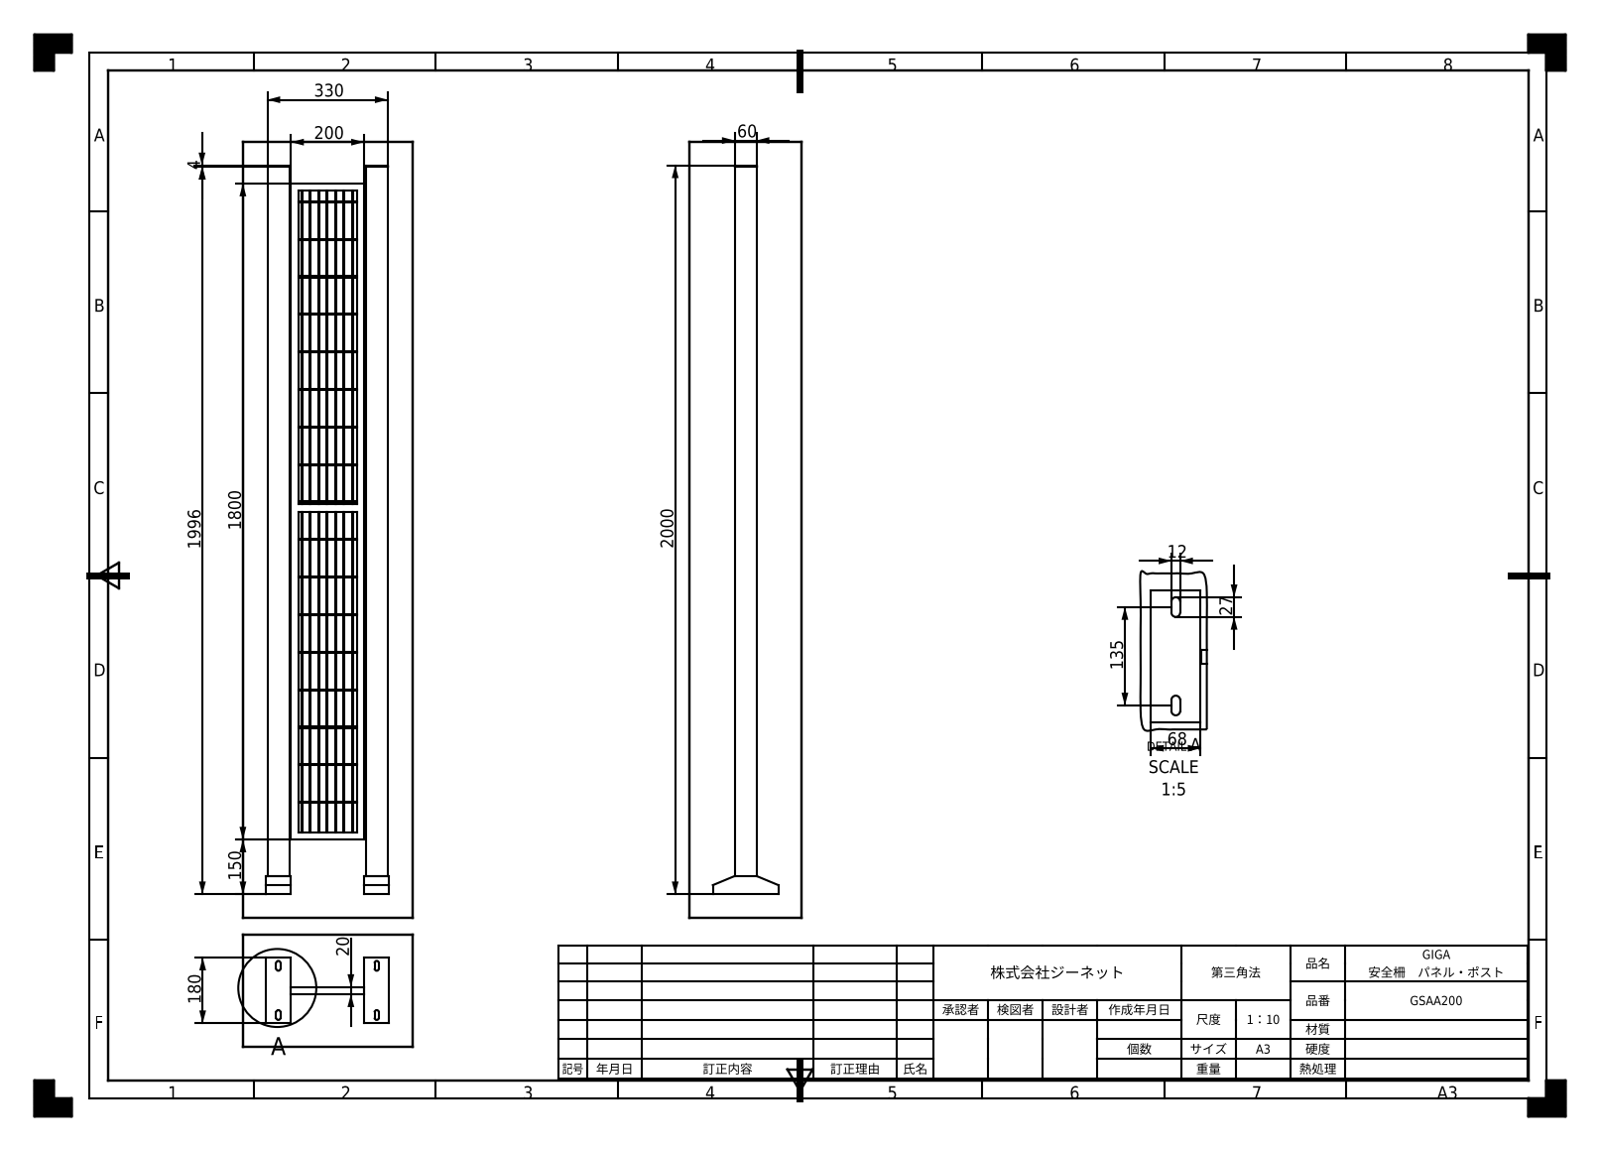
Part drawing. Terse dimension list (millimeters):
name: post; GSAA200_panel; GSAA200_202104
written by: SIEMENS PLM Software NX 12.0 (AUTOMOTIVE_DESIGN)
unit: mm
bodies: 29 solids, 144 faces (110 planar, 34 cylindrical, 0 other)
size: 2000 × 338 × 180
volume: 16 800 000 mm³; area: 1 520 000 mm²
bosses: 24× ⌀3
rounds: 8× R6
face distances: 60, 270, 20, 330, 210, 20.64, 39.36, 40.64, 19.36, 180
